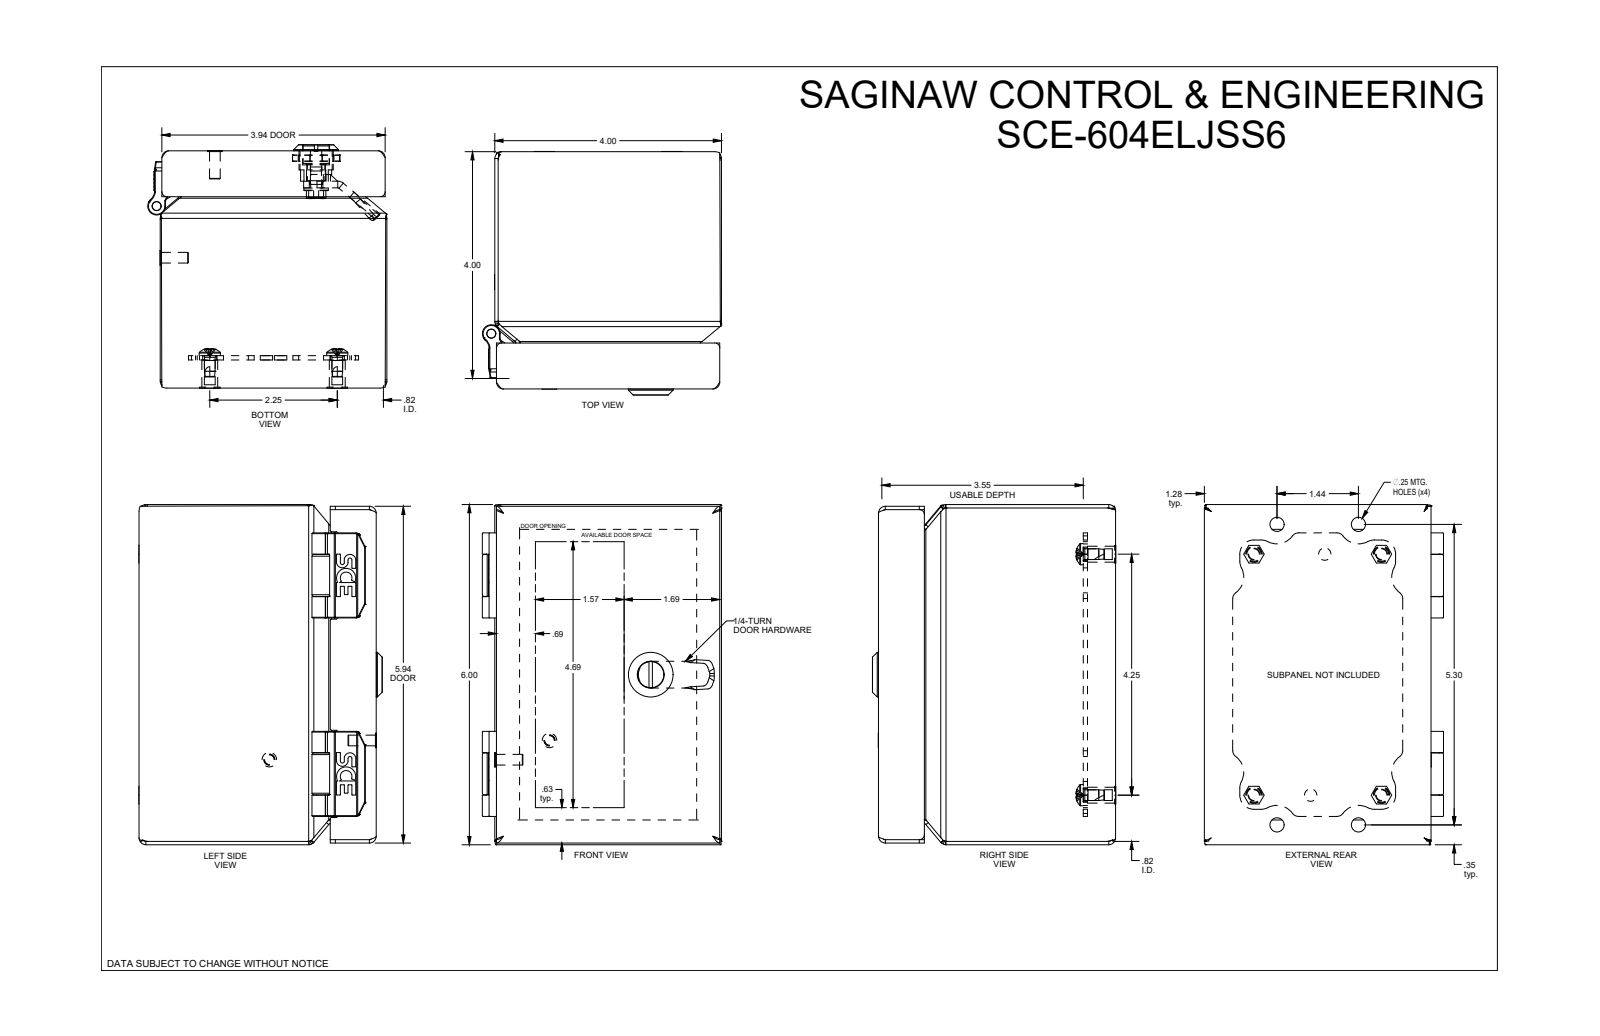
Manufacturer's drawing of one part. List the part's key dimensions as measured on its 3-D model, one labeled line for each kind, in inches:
Part name (STEP PRODUCT): SCE-604ELJSS6
STEP written by: SolidWorks 2019 (CONFIG_CONTROL_DESIGN)
Units: inches
Bodies: 0 solids, 2717 faces (863 planar, 790 cylindrical, 1064 other)
Overall size (bounding box): 6 × 4.296 × 4.22
Round holes (diameter × count): ⌀0.25 ×8, ⌀0.19 ×4, ⌀0.284 ×4, ⌀0.479 ×4, ⌀0.02 ×2, ⌀0.1 ×2, ⌀0.174 ×2, ⌀0.196 ×2, ⌀0.218 ×2, ⌀0.266 ×2, ⌀0.158 ×1, ⌀0.2 ×1
Round bosses / shafts (diameter × count): ⌀0.188 ×6, ⌀0.373 ×4, ⌀0.28 ×4, ⌀0.17 ×4, ⌀0.16 ×4, ⌀0.135 ×4, ⌀0.108 ×4, ⌀0.26 ×2
Partial cylindrical surfaces — rounded edges, fillets, slot ends (radius × count): R0.106 ×132, R0.005 ×131, R0.008 ×32, R0.008 ×26, R0.025 ×24, R0.03 ×24, R0.12 ×23, R0.06 ×22
Main face-to-face distances: 0.06, 0.06, 3.94, 5.94, 4.124, 4.065, 4.185, 4.125, 4, 3.88
Hole centre spacings: 3.5, 0.664, 1.917, 4.792, 5.119, 0.793, 0.994, 1
